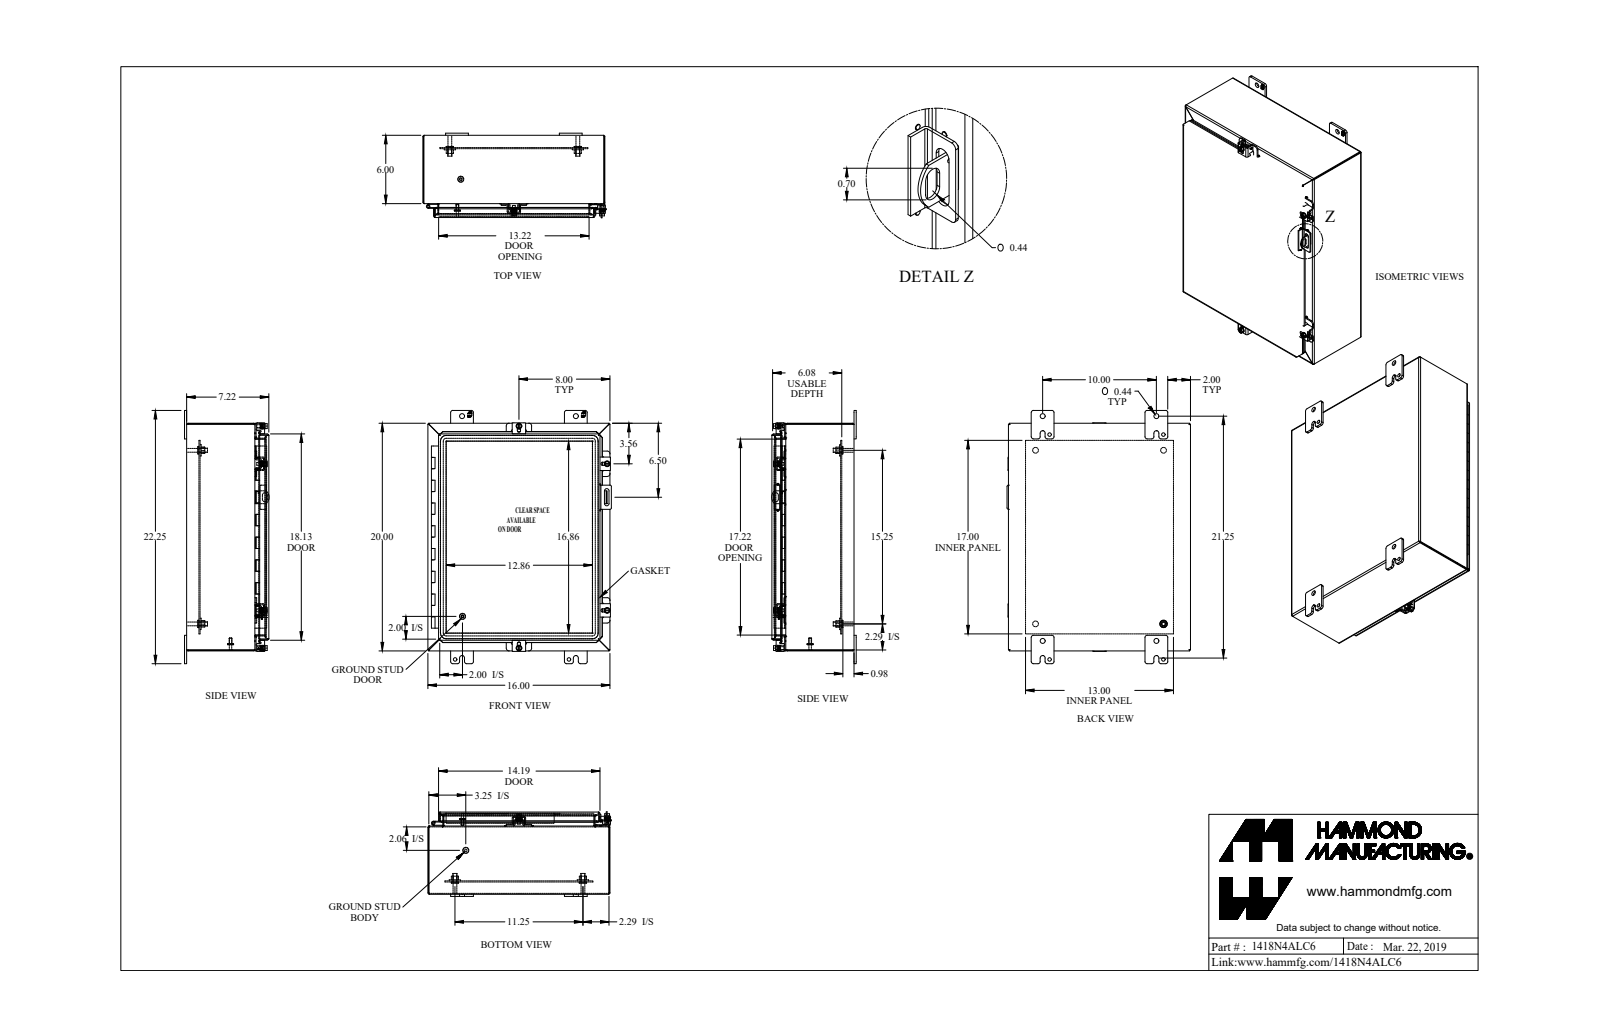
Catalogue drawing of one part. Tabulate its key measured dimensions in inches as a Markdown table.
| quantity | value |
| --- | --- |
| part name | 1418N4ALC6_Default |
| STEP written by | SolidWorks 2019 (CONFIG_CONTROL_DESIGN) |
| units | inches |
| bodies | 38 solids, 1478 faces (879 planar, 489 cylindrical, 110 other) |
| overall size | 22.25 × 16.126 × 7.437 |
| volume | 139.3 in³ |
| surface area | 3 216 in² |
| round holes (diameter × count) | 0.232 × 4, 0.265 × 4, 0.313 × 4, 0.375 × 4, 0.437 × 4, 0.5 × 4, 0.307 × 2, 0.445 × 2, 0.125 × 1, 0.187 × 1 |
| round bosses / shafts (diameter × count) | 0.131 × 12, 0.65 × 4, 0.5 × 4, 0.4 × 4, 0.375 × 4, 0.33 × 4, 0.244 × 4, 1 × 2 |
| partial cylindrical surfaces (radius × count) | 0.188 × 24, 0.05 × 22, 0.15 × 22, 0.25 × 20, 0.041 × 16, 0.122 × 16, 0.125 × 8, 0.141 × 8 |
| main face-to-face distances | 0.081, 0.1, 7.041, 7.122, 7.141, 7.222, 15.919, 0.095, 6.046, 5.946 |
| hole center spacings | 18.263, 1.736, 6.013, 10, 18.951, 19.75, 22.137, 2.434 |
